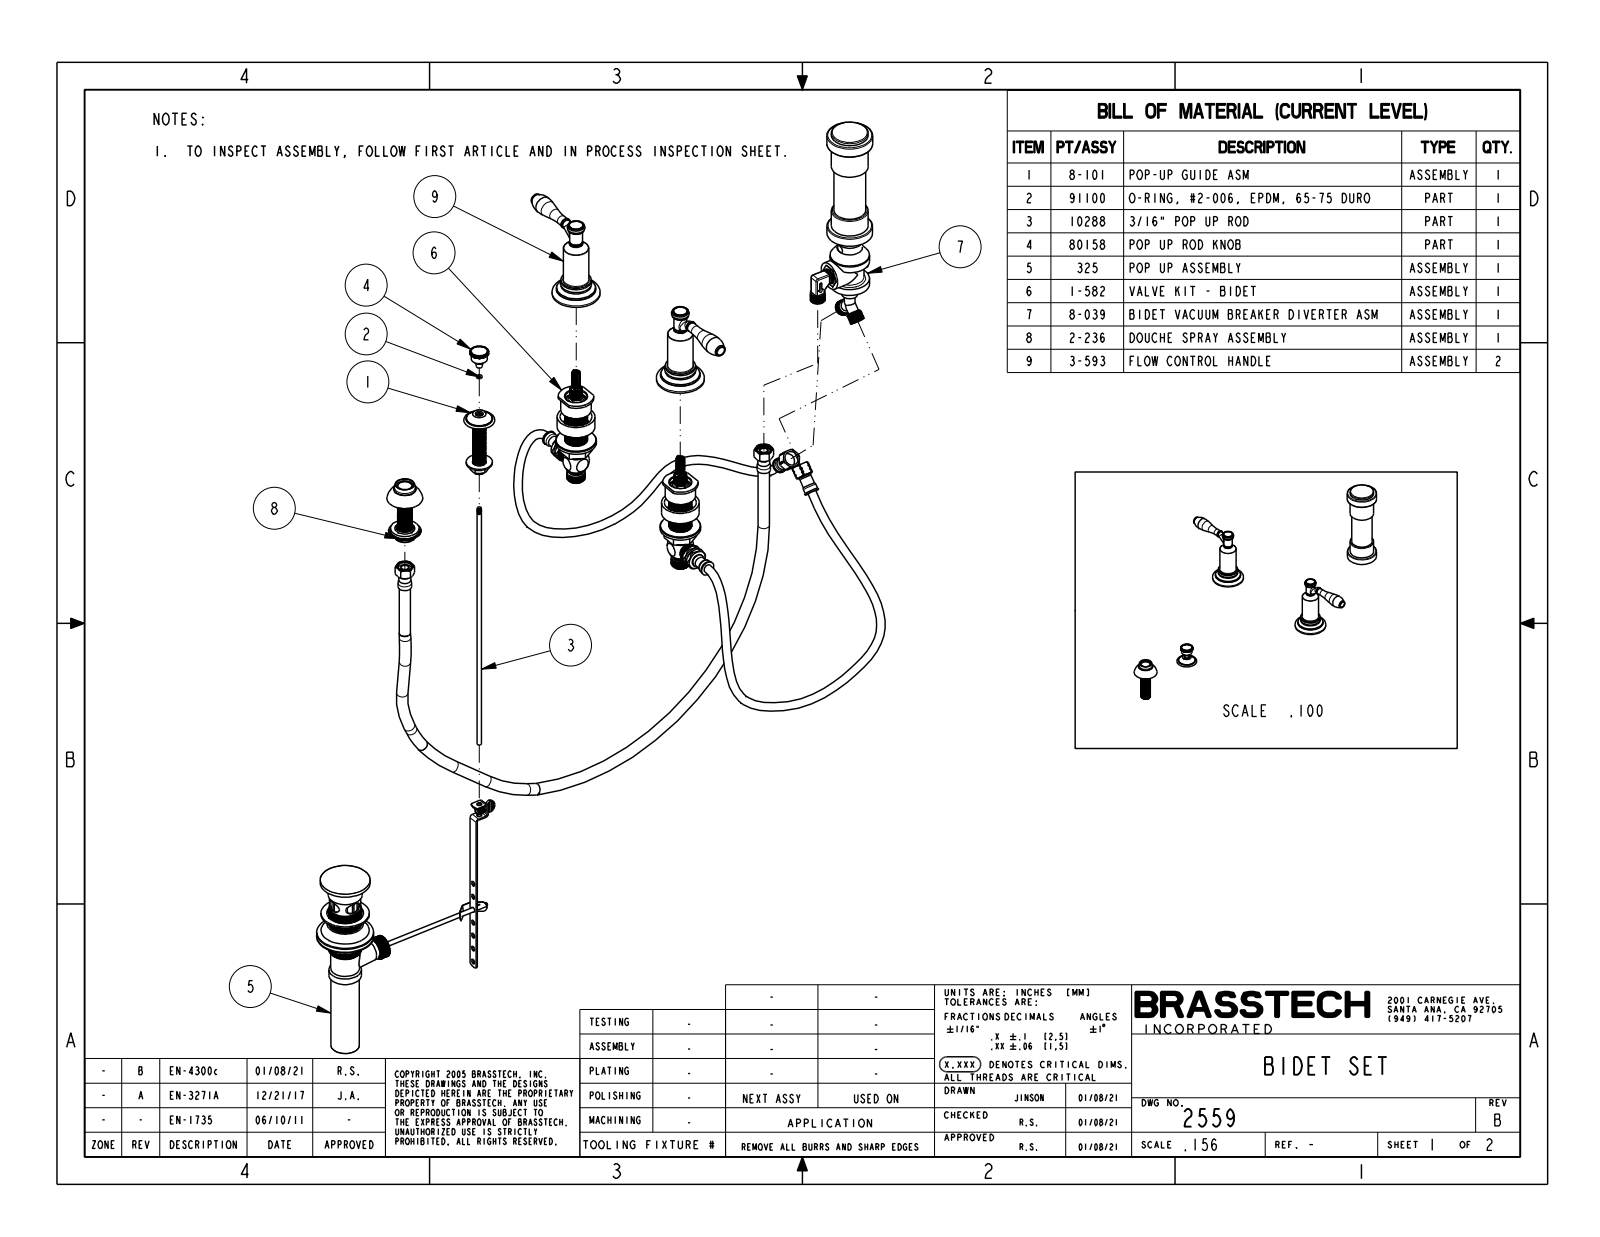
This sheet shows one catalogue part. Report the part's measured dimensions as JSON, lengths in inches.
{"part_name": "2559", "step_written_by": "CREO PARAMETRIC BY PTC INC, 2018400 (CONFIG_CONTROL_DESIGN)", "units": "inches", "bodies": {"solids": 5, "faces": 798, "planar": 243, "cylindrical": 225, "other": 330}, "overall_size": [22.8, 14.3, 5.445], "volume_in3": 21.18, "surface_area_in2": 99.15, "round_holes": [[0.625, 1], [0.792, 1], [0.94, 1]], "round_bosses_or_shafts": [[2.11, 2], [1.7, 2], [1.33, 2], [1.12, 2], [0.714, 2], [0.6, 2], [0.57, 2], [0.42, 2]], "partial_cylinders_radius": [[0.01, 90], [0.357, 1], [0.411, 1]], "face_to_face_distances": [5.445, 0.5, 4.545, 4.045, 5.295, 0.15, 4.795, 0.65, 0.42, 4.375]}
